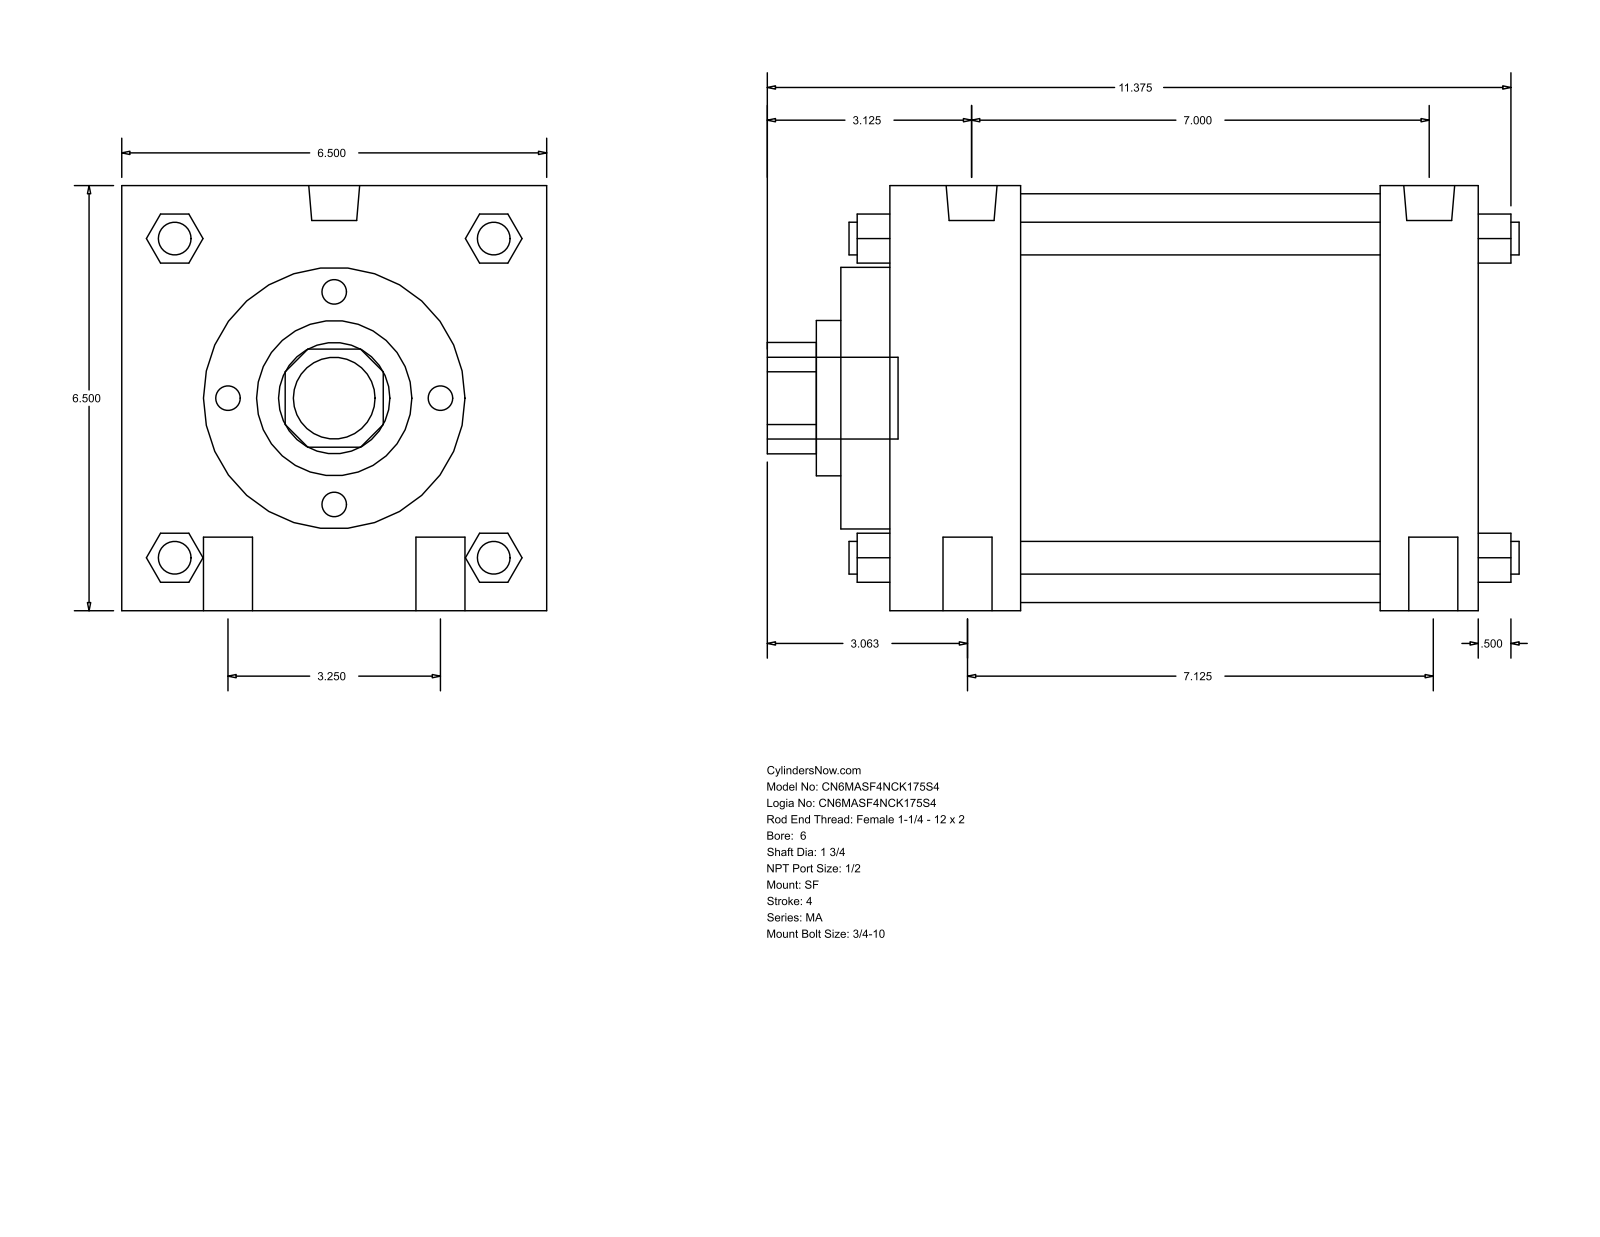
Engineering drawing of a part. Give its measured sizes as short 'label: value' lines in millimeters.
name: MA_SF__0600_1.75
written by: GSSL Pune (CONFIG_CONTROL_DESIGN)
unit: mm
bodies: 0 solids, 126 faces (95 planar, 31 cylindrical, 0 other)
size: 292.1 × 165.1 × 165.1
holes: 1× ⌀44.45, 1× ⌀60.33, 1× ⌀101.6, 1× ⌀158.75
bosses: 4× ⌀19.05, 4× ⌀12.7, 2× ⌀19.77, 2× ⌀17.46, 1× ⌀31.75
rounds: 1× R21.63
face distances: 165.1, 228.61, 19.05, 50.8, 190.5, 38.11, 139.7, 177.81, 69.85, 209.55
